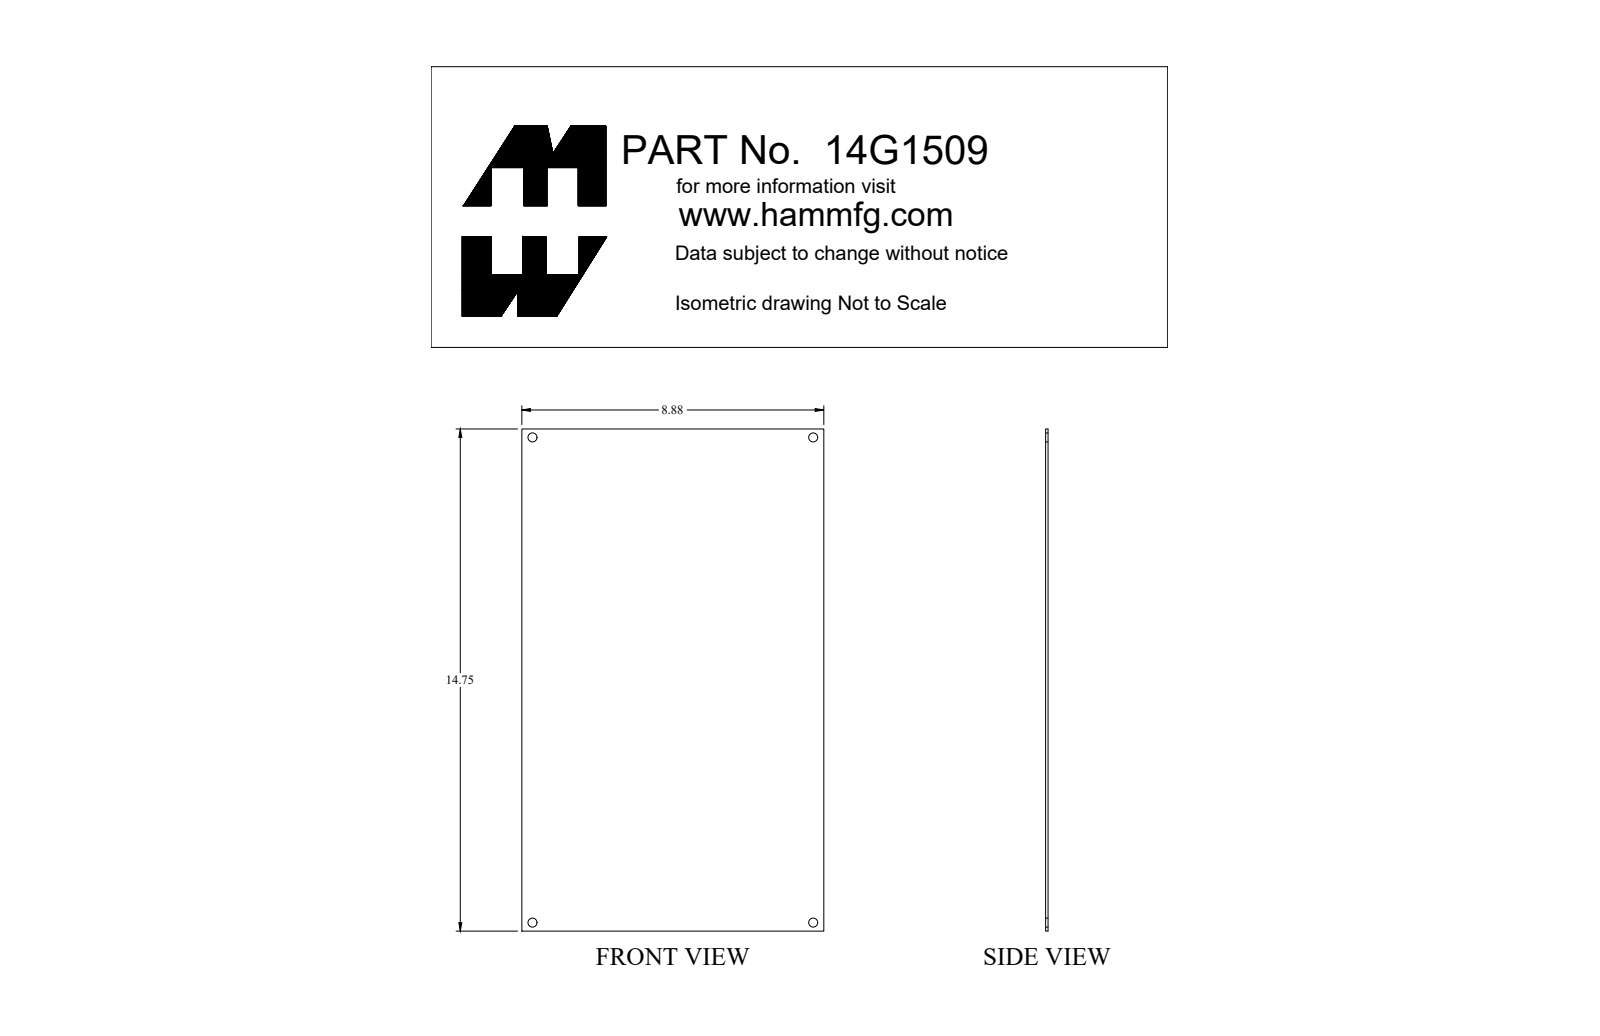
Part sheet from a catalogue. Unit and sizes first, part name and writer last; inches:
Units: inches
Overall size (bounding box): 14.75 × 8.875 × 0.072
Round holes (diameter × count): ⌀0.265 ×4
Main face-to-face distances: 0.072, 8.875, 14.75
Hole centre spacings: 8.25, 14.25, 16.465
Volume: 9.409 in³ · Surface area: 265 in²
Bodies: 1 solid, 10 faces (6 planar, 4 cylindrical, 0 other)
Part name (STEP PRODUCT): 14G1509
STEP written by: SolidWorks 2018 (AUTOMOTIVE_DESIGN)
